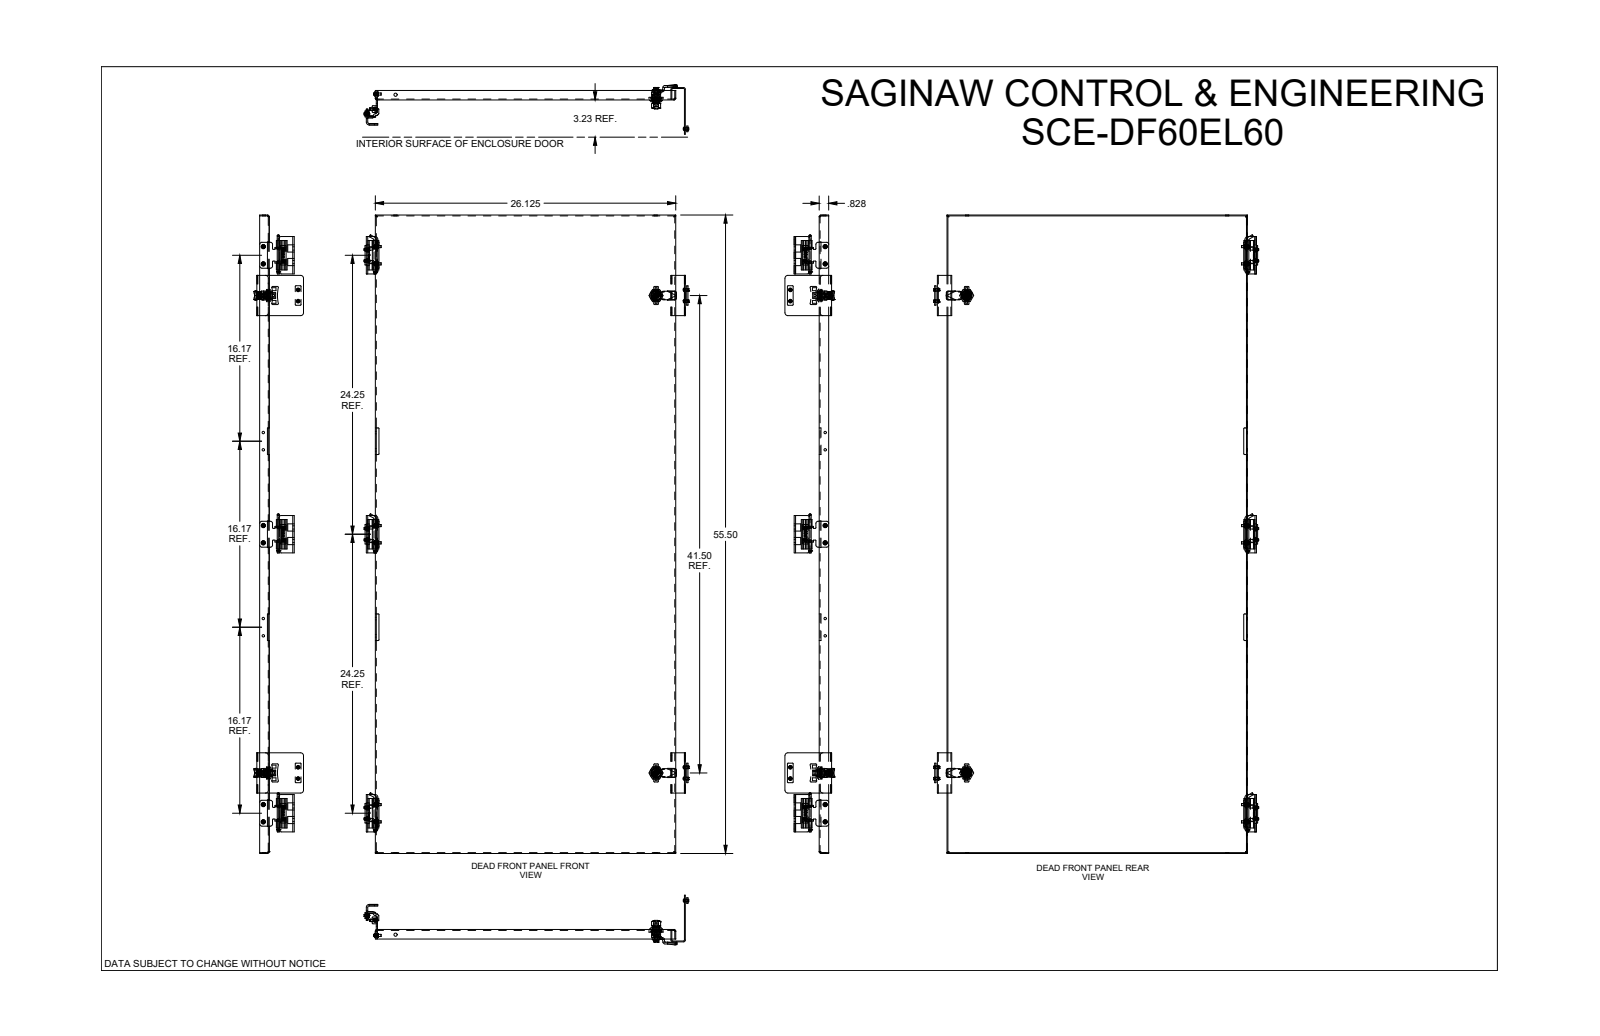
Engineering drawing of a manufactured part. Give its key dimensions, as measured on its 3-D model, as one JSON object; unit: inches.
{"part_name": "SCE-DF60EL60", "step_written_by": "SolidWorks 2021 (AUTOMOTIVE_DESIGN)", "units": "inches", "bodies": {"solids": 54, "faces": 2129, "planar": 1082, "cylindrical": 636, "other": 411}, "overall_size": [55.5, 28.243, 4.319], "volume_in3": 106.4, "surface_area_in2": 3413, "round_holes": [[0.172, 10], [0.244, 10], [0.19, 6], [0.21, 6], [0.25, 6], [0.266, 6], [0.197, 2], [0.315, 2], [0.394, 2], [0.433, 2], [0.634, 2], [0.222, 1]], "round_bosses_or_shafts": [[0.25, 10], [0.17, 10], [0.373, 6], [0.34, 6], [0.249, 6], [0.188, 6], [0.196, 4], [1.102, 2]], "partial_cylinders_radius": [[0.012, 54], [0.02, 22], [0.062, 22], [0.25, 21], [0.157, 16], [0.068, 9], [0.04, 8], [0.059, 8]], "face_to_face_distances": [0.06, 0.06, 26.065, 0.078, 26.125, 26.005, 55.44, 26.882, 26.822, 0.817], "hole_center_spacings": [24.25, 0.985, 1.749, 1.75, 2.13, 2.13, 48.5, 23.072]}
